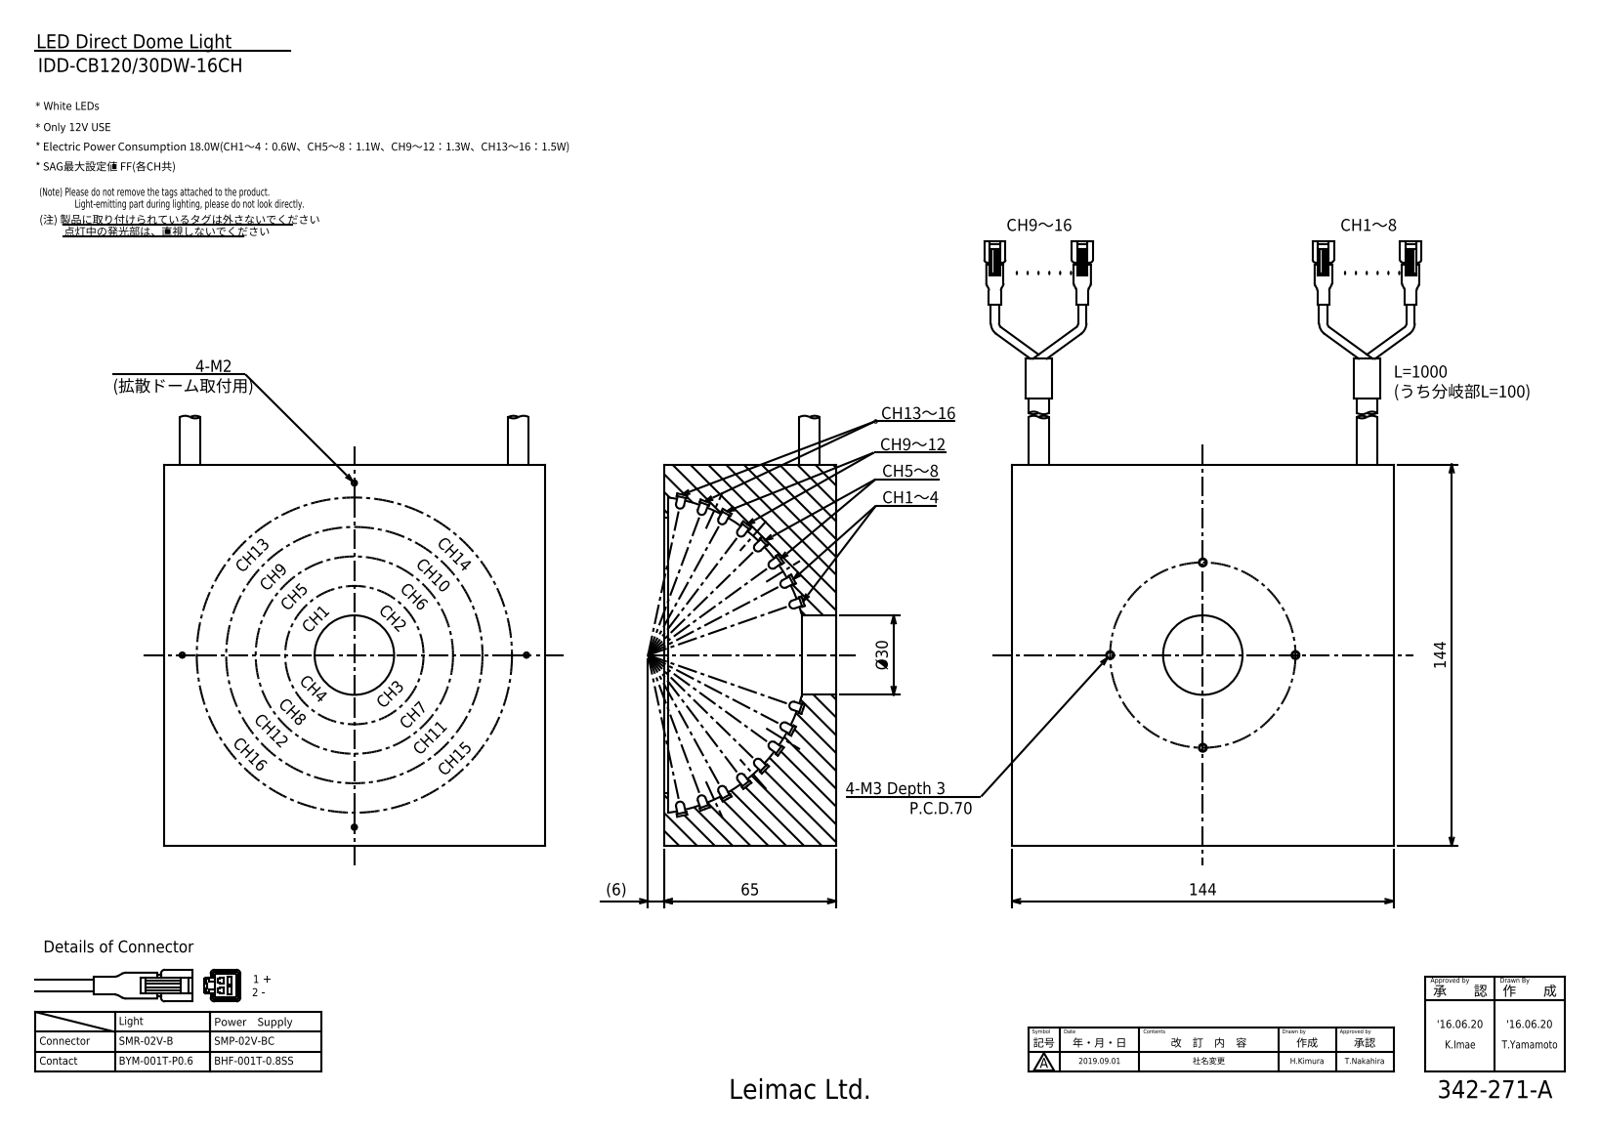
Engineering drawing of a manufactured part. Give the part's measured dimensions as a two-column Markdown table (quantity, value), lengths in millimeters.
| quantity | value |
| --- | --- |
| part name | IDD-CB120_30DW-16CH(外観図) |
| STEP written by | SolidWorks 2014 (CONFIG_CONTROL_DESIGN) |
| units | millimeters |
| bodies | 1 solid, 82 faces (23 planar, 38 cylindrical, 21 other) |
| overall size | 234.59 × 147.7 × 65 |
| volume | 1 044 000 mm³ |
| surface area | 93 756 mm² |
| round holes (diameter × count) | 1.6 × 4, 2.5 × 4, 30 × 1, 113 × 1 |
| round bosses / shafts (diameter × count) | 3.7 × 12, 8 × 2, 7.7 × 2 |
| partial cylindrical surfaces (radius × count) | 1.5 × 12 |
| main face-to-face distances | 144, 65, 1.5, 63.5, 58.5, 202.5, 32.09, 90.59, 234.59, 53.9 |
| hole center spacings | 73.82, 30, 35, 49.5, 65, 91.92, 100, 70 |
